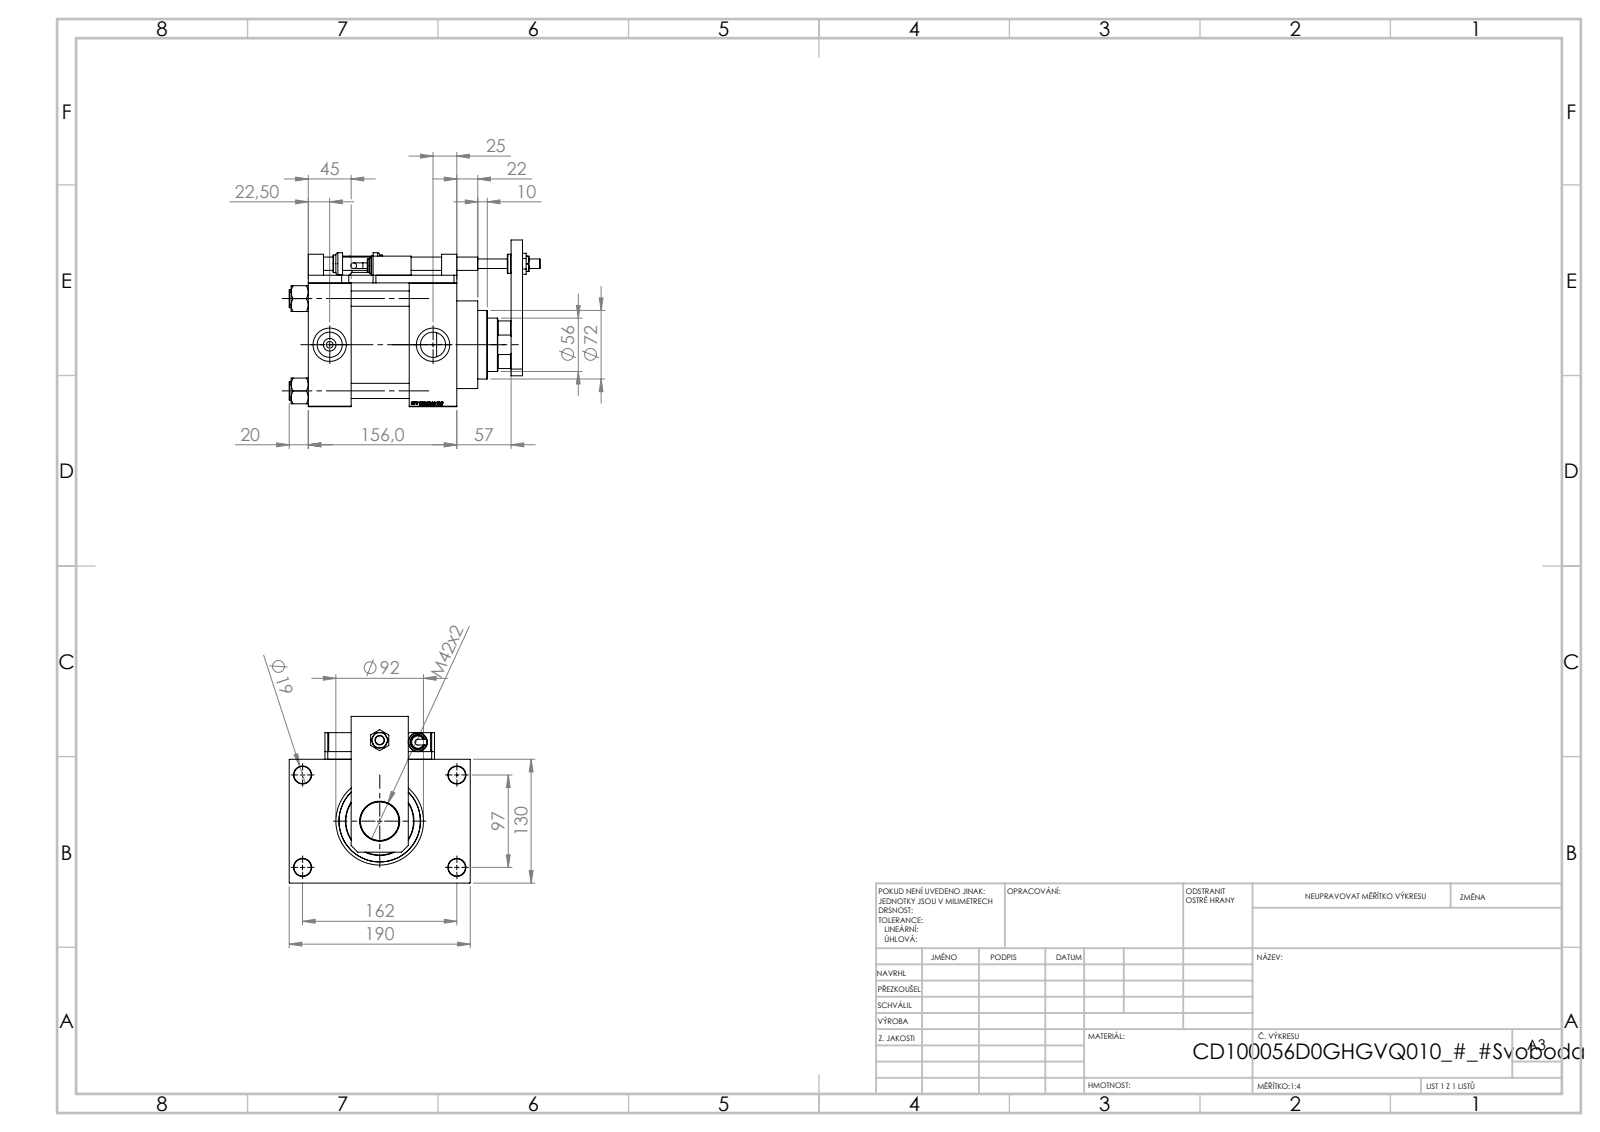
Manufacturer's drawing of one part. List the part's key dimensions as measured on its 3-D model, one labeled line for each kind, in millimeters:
Part name (STEP PRODUCT): V215CD_VC_A; V215CD_VCP_D; V215CD_SWITCH_Q_BLOK; V215CD_SWITCH_Q_PODLOZKA_FRONT (+7 more)
STEP written by: SolidWorks 2019 (CONFIG_CONTROL_DESIGN)
Units: millimetres
Bodies: 24 solids, 1379 faces (666 planar, 156 cylindrical, 557 other)
Overall size (bounding box): 263.5 × 190 × 175
Volume: 2 907 000 mm³ · Surface area: 448 176 mm²
Round holes (diameter × count): ⌀8.5 ×4, ⌀13.5 ×4, ⌀16 ×4, ⌀18 ×4, ⌀7 ×2, ⌀26.44 ×2, ⌀35 ×2, ⌀10 ×1, ⌀14 ×1, ⌀40.5 ×1, ⌀42 ×1, ⌀56 ×1
Round bosses / shafts (diameter × count): ⌀19 ×4, ⌀20 ×3, ⌀16 ×2, ⌀14 ×2, ⌀6 ×2, ⌀106 ×1, ⌀92 ×1, ⌀72 ×1
Partial cylindrical surfaces — rounded edges, fillets, slot ends (radius × count): R7.5 ×4, R27 ×1
Main face-to-face distances: 45, 130, 8, 111, 106, 156, 50, 61, 138, 30
Hole centre spacings: 32.55, 68.52, 94.41, 96.9, 102.27, 129.45, 161.73, 32
